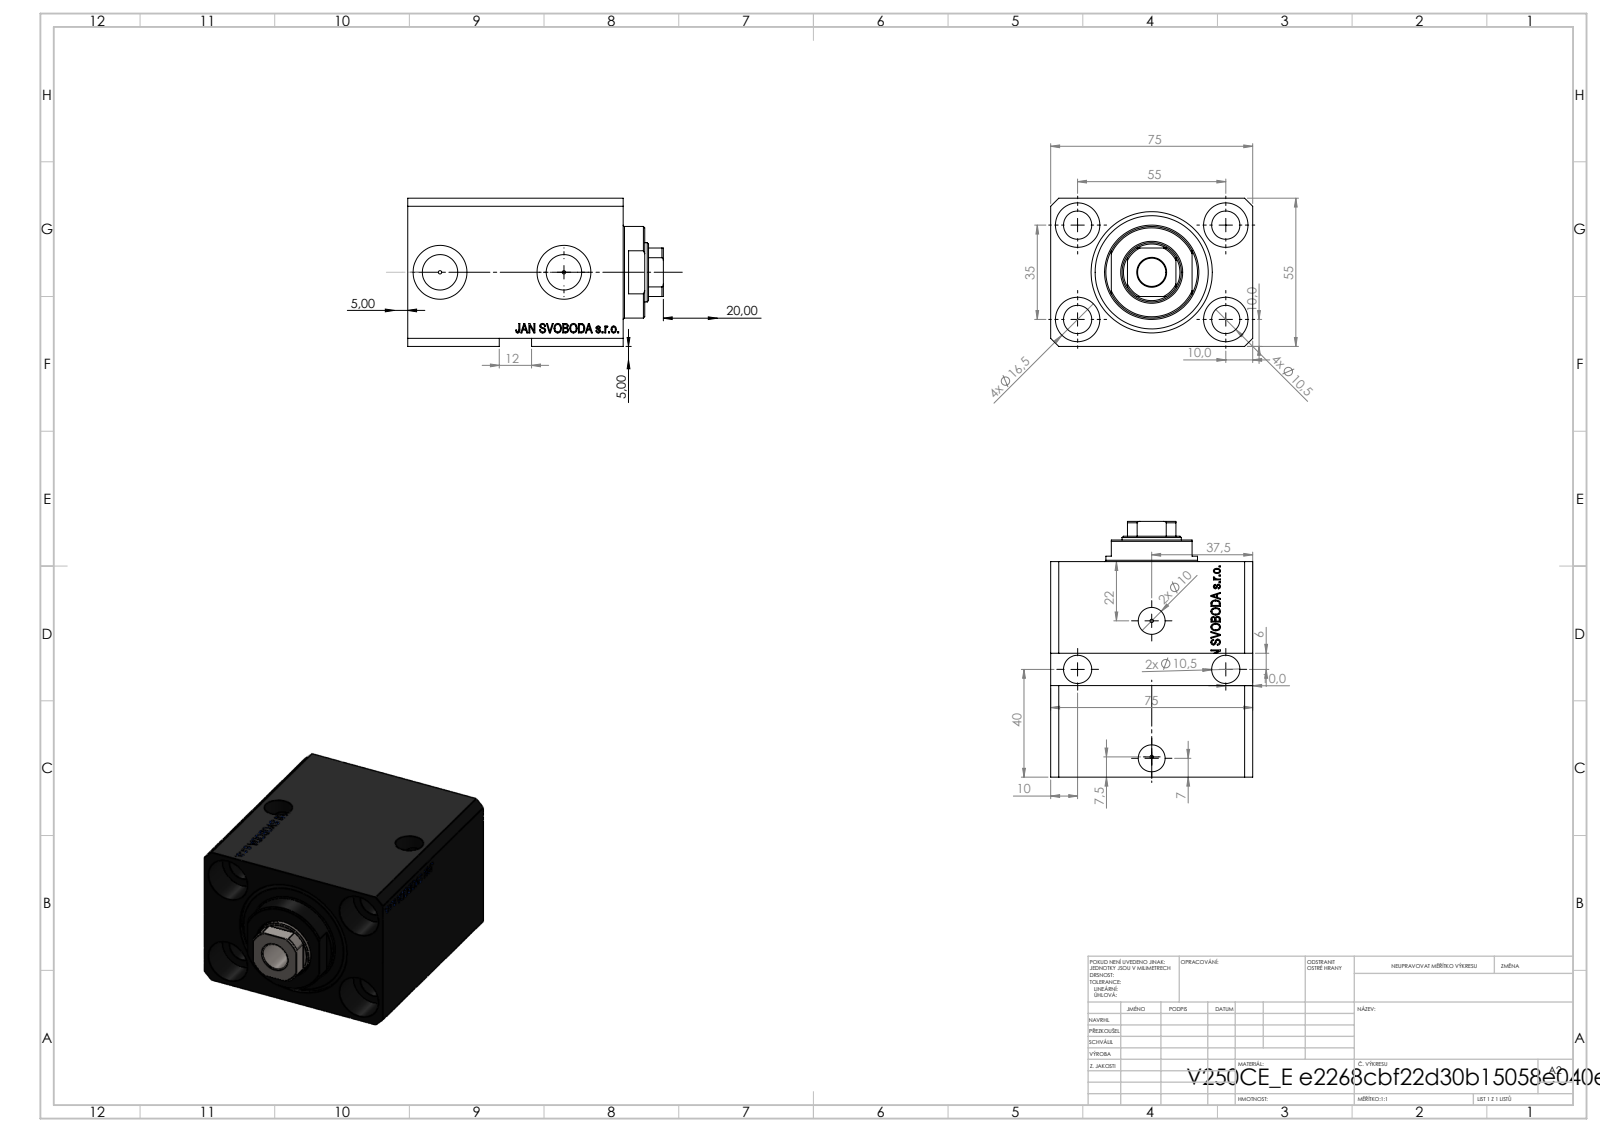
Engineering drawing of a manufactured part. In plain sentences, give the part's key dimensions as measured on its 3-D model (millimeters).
The part is named "V250CE_VC_E; V250CE_E_Body; V250CE_C_VCP". Its 3-D file was written by "SolidWorks 2019 (CONFIG_CONTROL_DESIGN)". It is 3 solids with 894 faces: 438 planar, 84 cylindrical and 372 other. Overall it measures 95 by 75 by 55 millimeters. Its volume is 275 455 cubic millimeters and its surface area 67 234 square millimeters. Round holes: 7 of diameter 10.5, 4 of diameter 1.25, 4 of diameter 16.5, 2 of diameter 10, 2 of diameter 13.16, 2 of diameter 20, 1 of diameter 22, 1 of diameter 32, 1 of diameter 45. Round bosses or shafts: 1 of diameter 34. Partial cylindrical surfaces (rounded edges, fillets, slot ends): 1 of radius 10.5. The main face-to-face distances are 55, 75, 15, 80, 65, 9.9, 55.1, 70.1, 11, 69. The hole center spacings are 32.6, 55, 32.87, 35, 42.55, 42.96, 65.19, 0.53.
